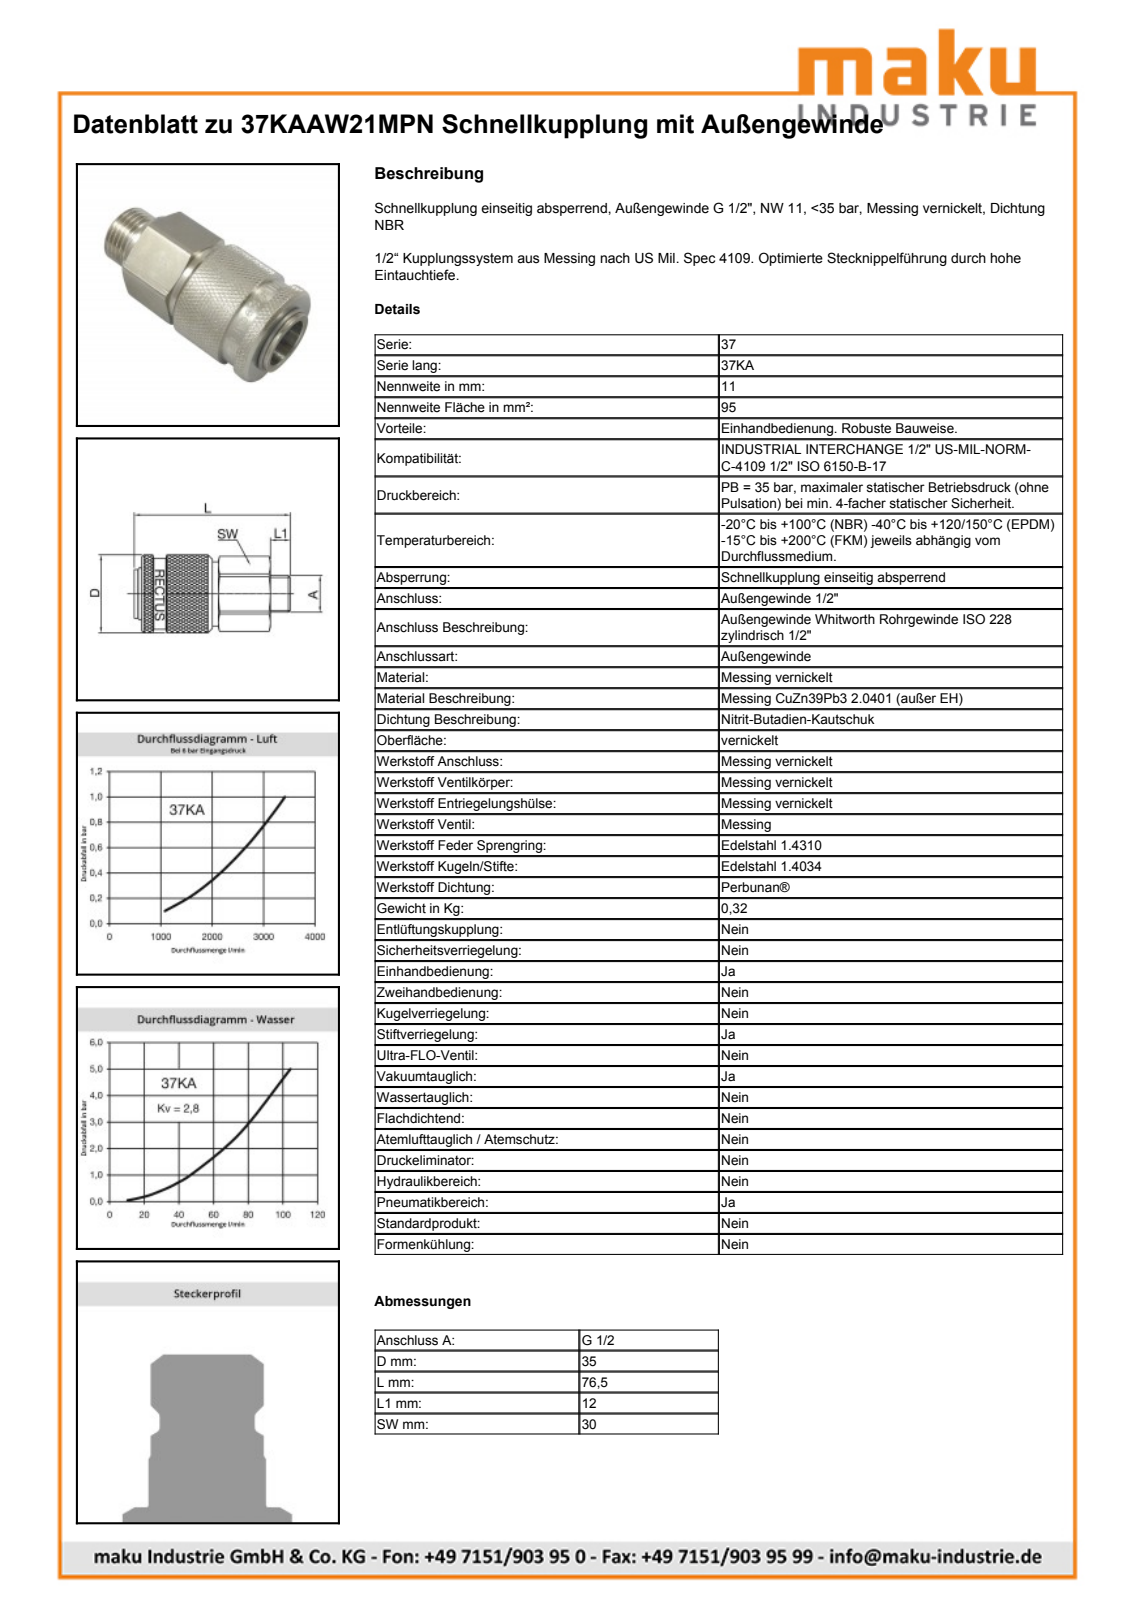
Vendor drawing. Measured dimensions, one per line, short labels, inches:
name: D106867
written by: Autodesk Inventor 2013 (AUTOMOTIVE_DESIGN)
unit: in
bodies: 1 solid, 499 faces (173 planar, 60 cylindrical, 266 other)
size: 2.874 × 1.386 × 1.386
volume: 2.961 in³; area: 22.85 in²
holes: 1× ⌀0.866, 1× ⌀0.945, 1× ⌀1.15, 1× ⌀1.177
bosses: 1× ⌀1.386, 1× ⌀1.26, 1× ⌀1.142, 1× ⌀1.024, 1× ⌀0.944, 1× ⌀0.882, 1× ⌀0.87, 1× ⌀0.825
rounds: 1× R0.626, 1× R0.667
face distances: 0.126, 1.182, 1.181, 1.18, 2.874, 2.748, 1.299, 1.575, 2.283, 2.157
